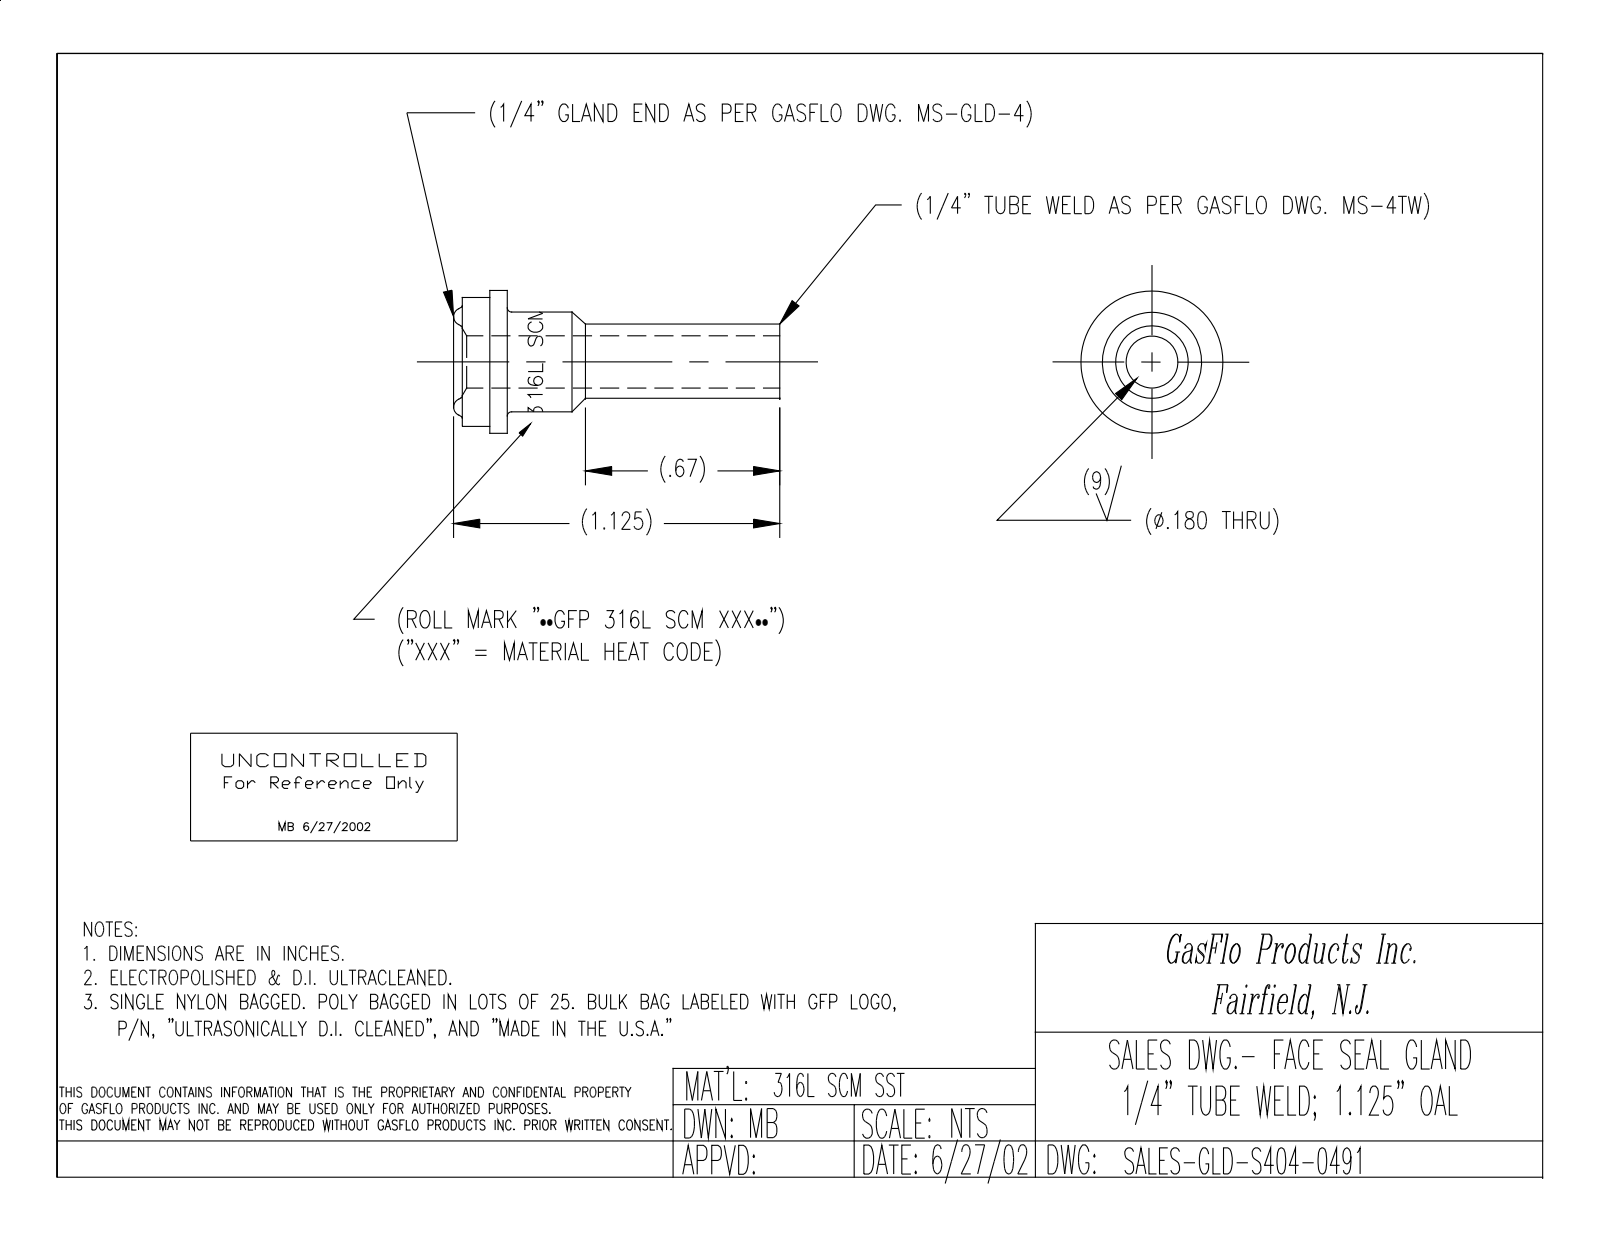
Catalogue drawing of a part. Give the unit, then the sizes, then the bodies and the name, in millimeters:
Units: millimetres
Overall size (bounding box): 28.6 × 12.5 × 12.5
Round holes (diameter × count): ⌀4.5 ×1
Round bosses / shafts (diameter × count): ⌀12.5 ×1, ⌀11.3 ×1, ⌀8.9 ×1, ⌀6.4 ×1
Main face-to-face distances: 4.7, 1.5, 3.2, 23.9, 25.4, 28.6
Volume: 1 000 mm³ · Surface area: 1 301 mm²
Bodies: 1 solid, 18 faces (4 planar, 10 cylindrical, 4 other)
Part name (STEP PRODUCT): GLD-S404-0491
STEP written by: SolidWorks 2011 (CONFIG_CONTROL_DESIGN)
